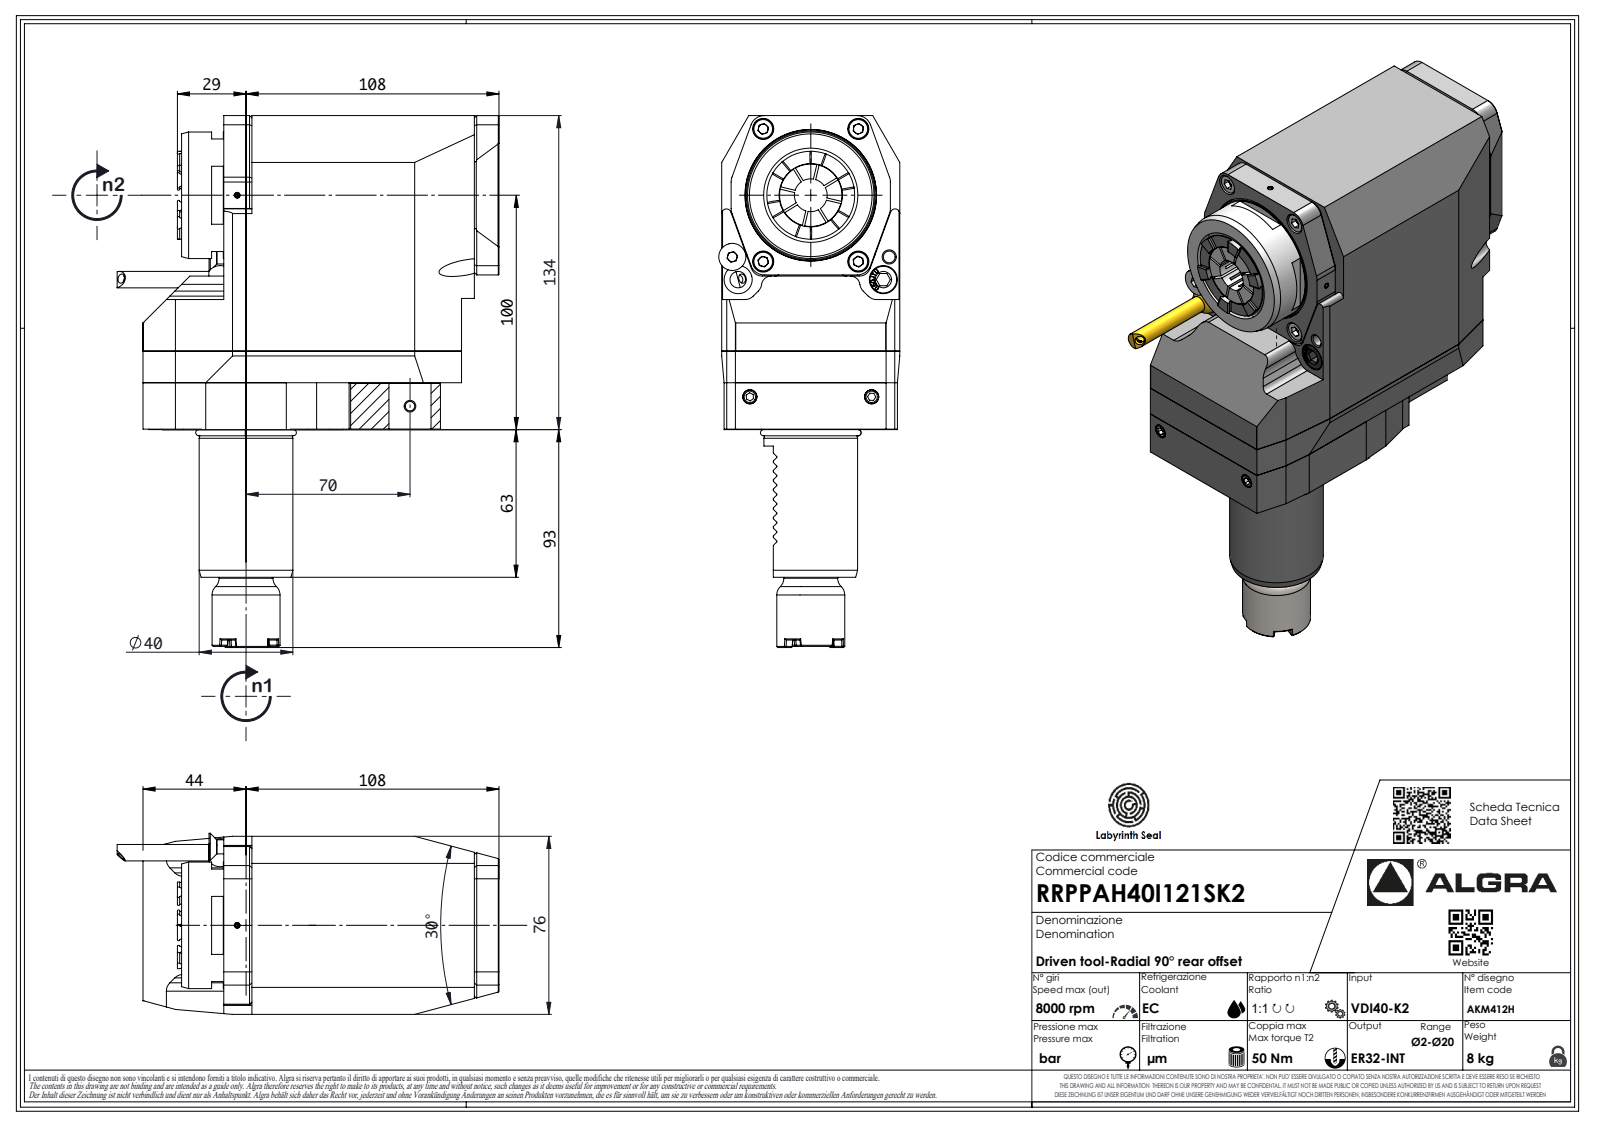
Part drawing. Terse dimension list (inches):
name: RRPPAH40I121SK2
written by: SolidWorks 2023 (AUTOMOTIVE_DESIGN)
unit: in
bodies: 1 solid, 658 faces (431 planar, 81 cylindrical, 146 other)
size: 8.937 × 6.437 × 2.992
volume: 78.96 in³; area: 140.8 in²
holes: 1× ⌀0.083, 1× ⌀0.787
bosses: 1× ⌀2.126, 1× ⌀1.575, 1× ⌀1.524, 1× ⌀1.142, 1× ⌀0.906, 1× ⌀0.276, 1× ⌀0.251, 1× ⌀0.067
rounds: 10× R0.012, 10× R0.236, 7× R0.013, 7× R0.02, 7× R0.146, 6× R0.197, 2× R0.079, 2× R0.157
face distances: 2.992, 5.276, 0.65, 5.354, 0.787, 4.488, 0.709, 0.778, 6.004, 1.358
